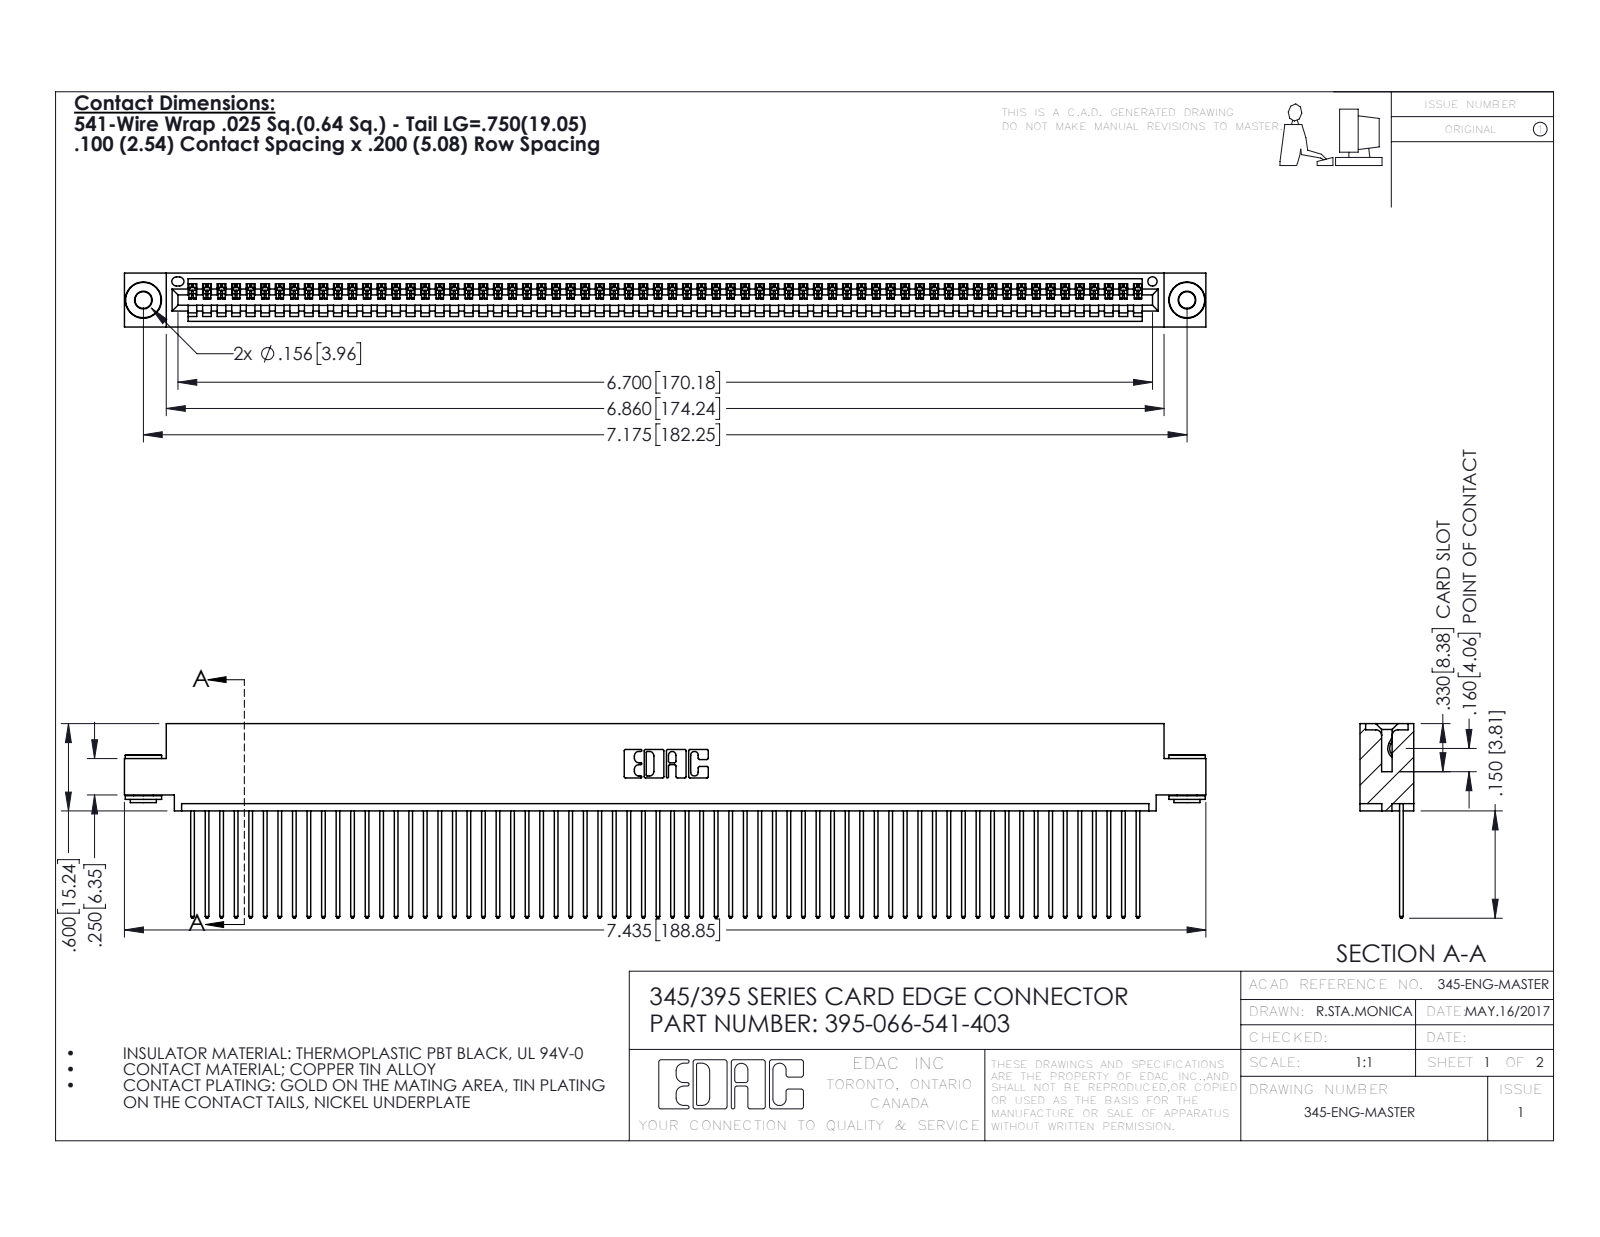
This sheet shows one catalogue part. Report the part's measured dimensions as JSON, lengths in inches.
{"part_name": "395-066-541-403; 345-250-002_345-250-002-102; 345-292-001_345-293-141; 345 Part_0.110 Offset - 0.156 Dia-TH", "step_written_by": "SolidWorks 2016 (CONFIG_CONTROL_DESIGN)", "units": "inches", "bodies": {"solids": 69, "faces": 3996, "planar": 2734, "cylindrical": 1254, "other": 8}, "overall_size": [7.435, 1.337, 0.37], "volume_in3": 1.117, "surface_area_in2": 40.64, "round_holes": [[0.116, 2], [0.156, 2], [0.064, 1]], "round_bosses_or_shafts": [[0.25, 2], [0.18, 2], [0.136, 2]], "partial_cylinders_radius": [[0.006, 132], [0.01, 132], [0.01, 22], [0.007, 6], [0.031, 6], [0.026, 3], [0.031, 2], [0.04, 2]], "face_to_face_distances": [0.072, 0.298, 0.025, 0.098, 0.272, 0.37, 0.2, 0.225, 0.149, 0.072], "hole_center_spacings": [0.27, 6.939, 7.175]}
